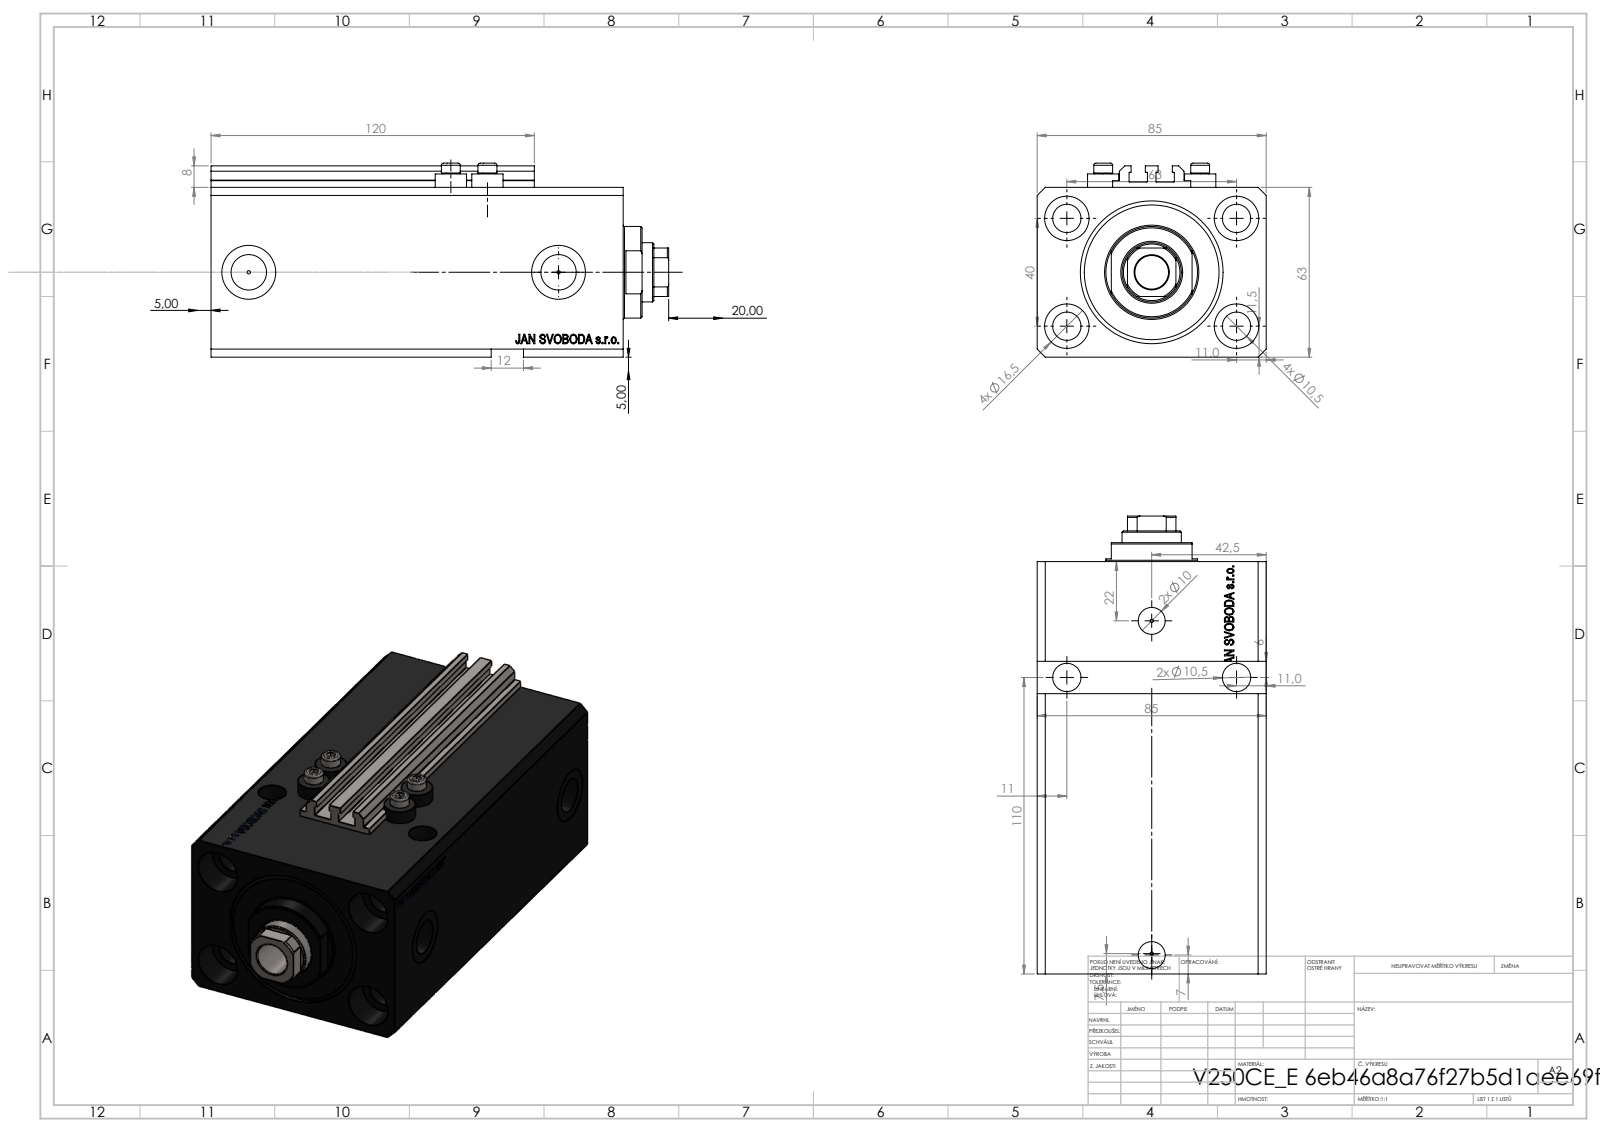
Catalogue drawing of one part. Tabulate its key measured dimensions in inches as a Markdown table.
| quantity | value |
| --- | --- |
| part name | ALLEN BOLT V250CE; V250CE_VC_E; V250CE_E_Body; V250CE_C_VCP |
| STEP written by | SolidWorks 2019 (CONFIG_CONTROL_DESIGN) |
| units | inches |
| bodies | 8 solids, 1123 faces (539 planar, 158 cylindrical, 426 other) |
| overall size | 6.693 × 3.346 × 2.835 |
| volume | 41.51 in³ |
| surface area | 220.1 in² |
| round holes (diameter × count) | 0.413 × 8, 0.049 × 4, 0.157 × 4, 0.65 × 4, 0.394 × 2, 0.518 × 2, 0.787 × 2, 0.492 × 1, 0.866 × 1, 1.575 × 1, 2.087 × 1 |
| round bosses / shafts (diameter × count) | 0.457 × 4, 0.276 × 4, 1.339 × 1 |
| partial cylindrical surfaces (radius × count) | 0.008 × 10, 0.413 × 1 |
| main face-to-face distances | 2.48, 3.346, 6.024, 0.669, 5.354, 0.449, 4.906, 5.575, 2.559, 0.118 |
| hole center spacings | 1.469, 2.48, 0.535, 0.606, 0.983, 1.324, 1.417, 1.491 |
